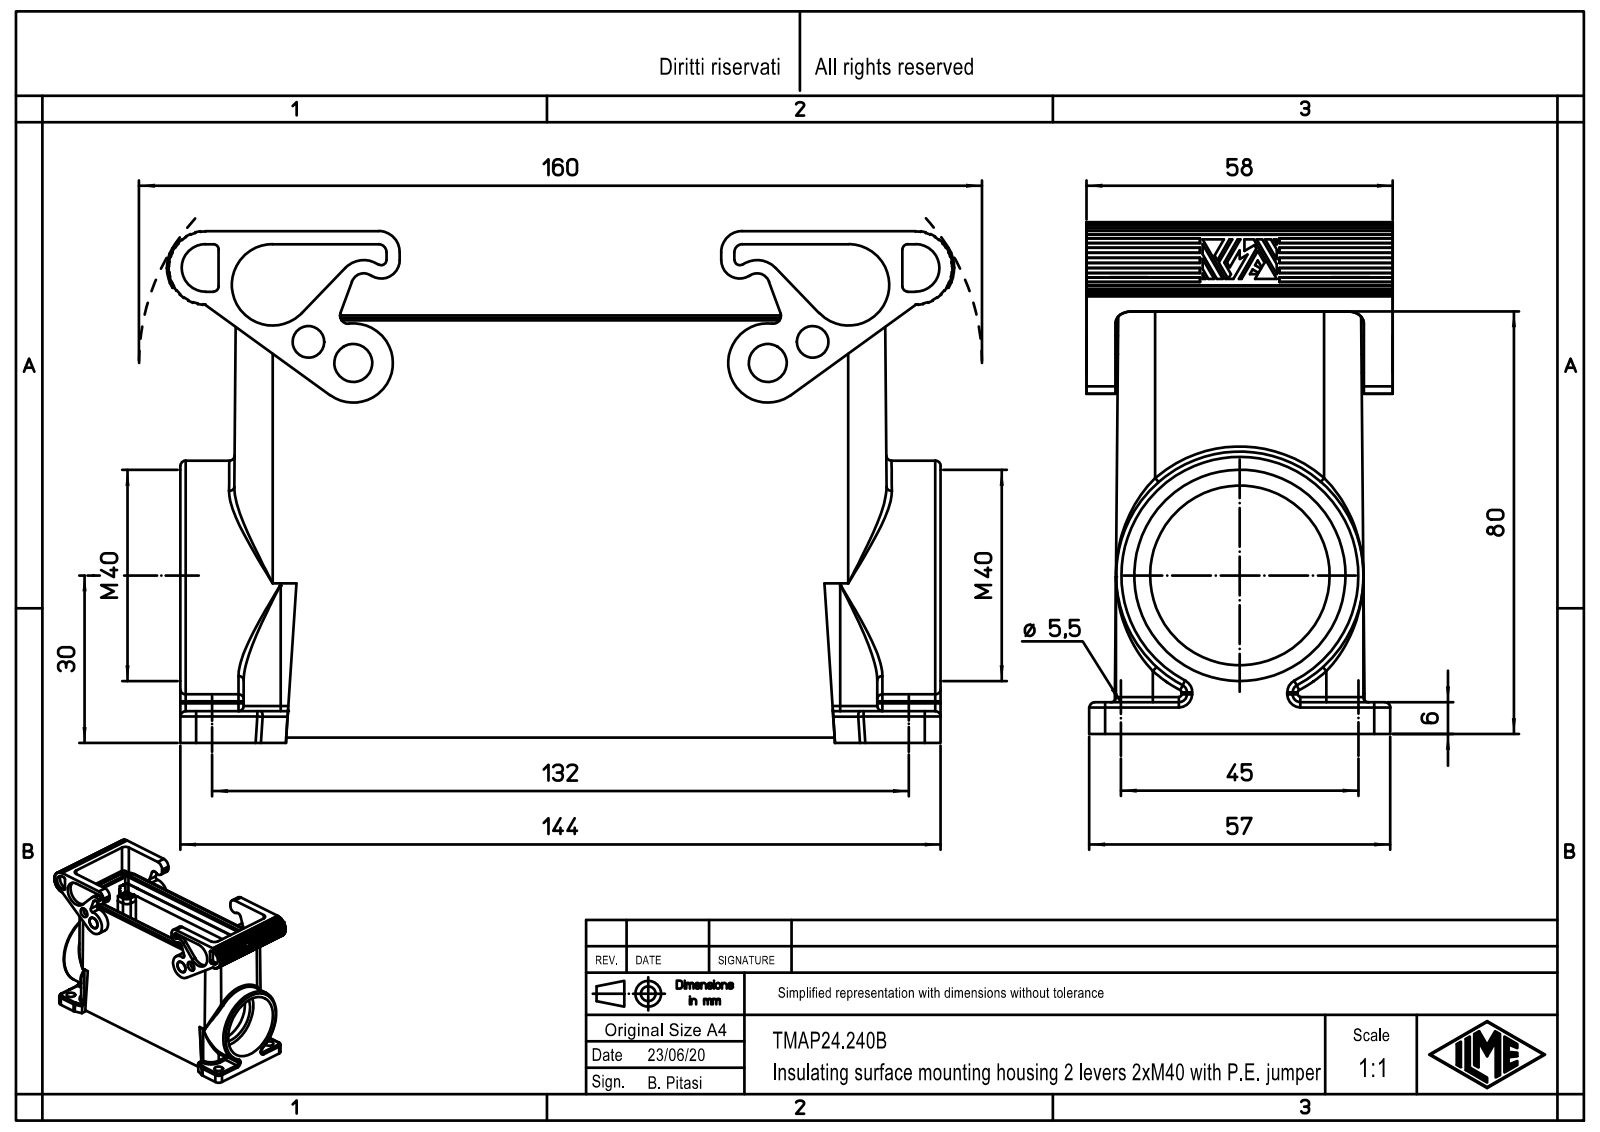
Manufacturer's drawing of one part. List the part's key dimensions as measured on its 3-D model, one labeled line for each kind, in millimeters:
Part name (STEP PRODUCT): TMAP24.240B
STEP written by: Creo Elements/Direct Modeling 20.1B 02-Apr-2019 (C) Parametric Technology GmbH (AUTOMOTIVE_DESIGN)
Units: millimetres
Bodies: 1 solid, 975 faces (561 planar, 282 cylindrical, 132 other)
Overall size (bounding box): 149.1 × 96.9 × 58
Volume: 214 105 mm³ · Surface area: 86 574 mm²
Round holes (diameter × count): ⌀3 ×4, ⌀3.5 ×4, ⌀5.5 ×4, ⌀6 ×2, ⌀10 ×2, ⌀34 ×1, ⌀40 ×1
Round bosses / shafts (diameter × count): ⌀4.8 ×4, ⌀7 ×2, ⌀46.87 ×1
Partial cylindrical surfaces — rounded edges, fillets, slot ends (radius × count): R1 ×22, R1.5 ×20, R3 ×12, R3.5 ×6, R7 ×6, R0.5 ×4, R1.3 ×4, R1.6 ×4
Main face-to-face distances: 40.6, 5.5, 6.5, 1, 52.5, 8.75, 2.5, 55.5, 40.4, 12.1
Hole centre spacings: 16.64, 38.63, 118.34, 123.37, 9.39, 27, 45, 87.09
